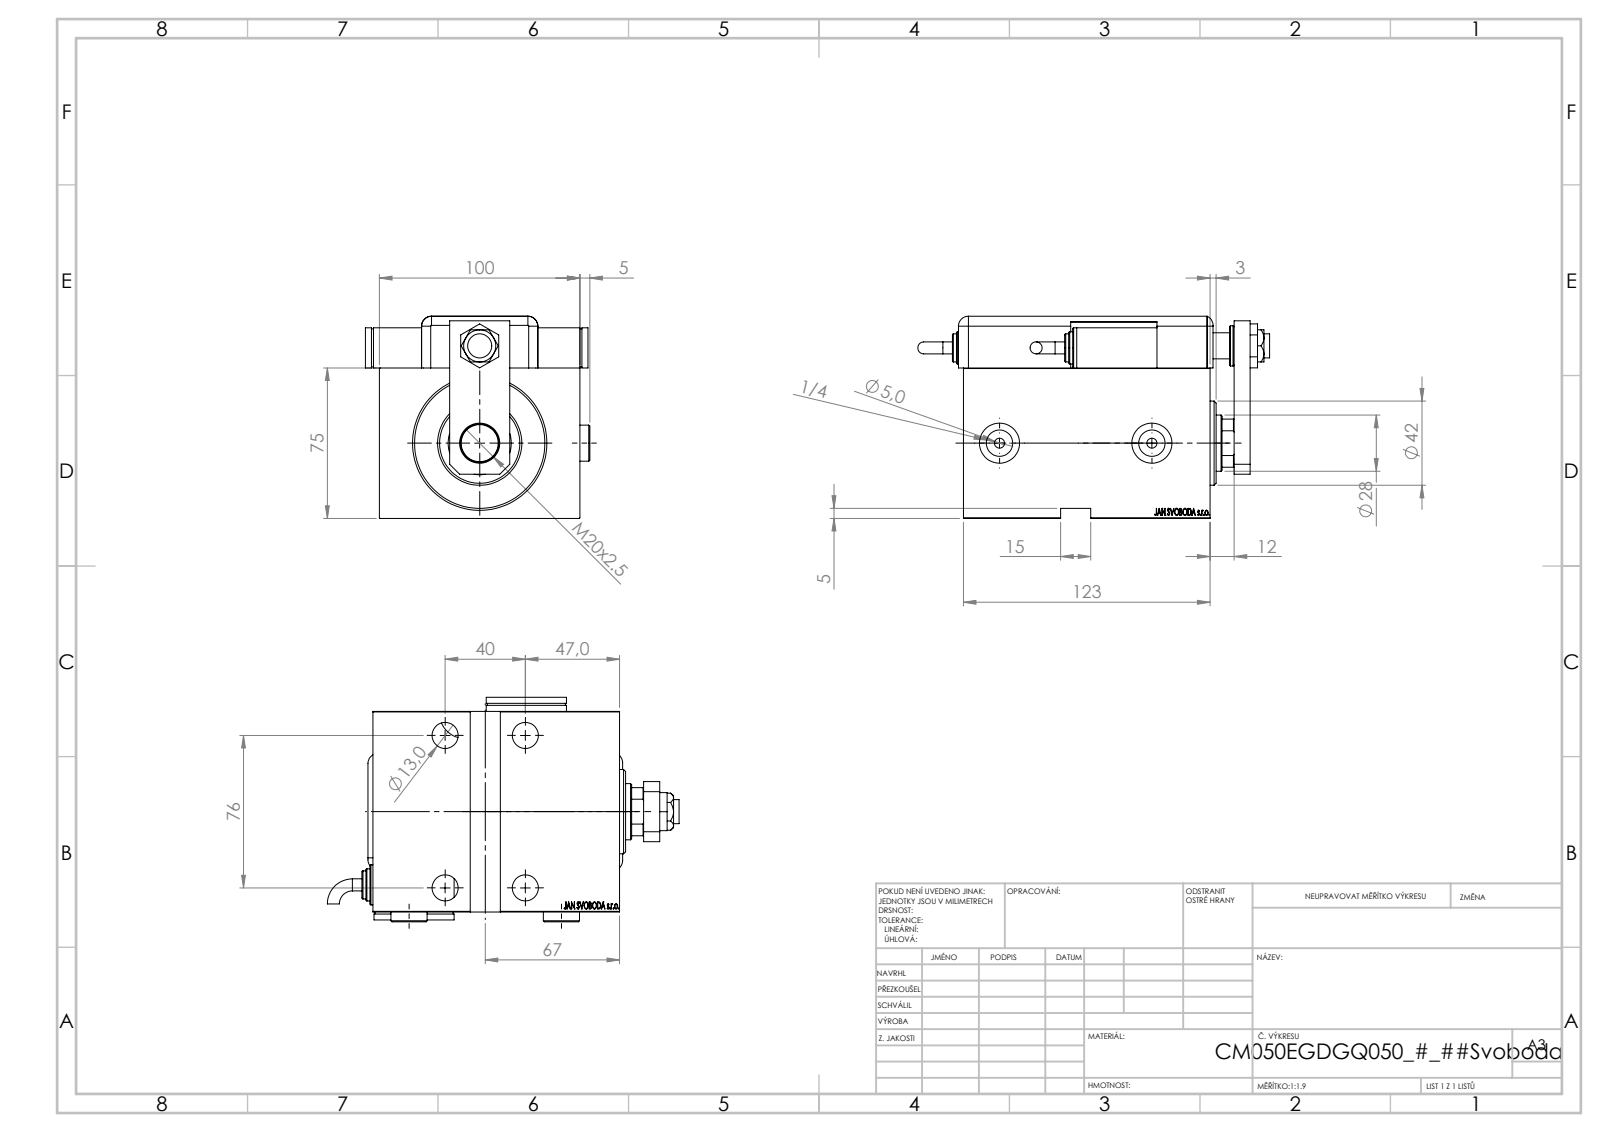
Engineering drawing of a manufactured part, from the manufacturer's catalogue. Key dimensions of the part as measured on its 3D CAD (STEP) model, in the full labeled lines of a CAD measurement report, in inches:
Part name (STEP PRODUCT): NUT_D19; KRYT; SWITCH Q; SWITCH DIM A_G (+8 more)
STEP written by: SolidWorks 2019 (CONFIG_CONTROL_DESIGN)
Units: inches
Bodies: 15 solids, 1296 faces (652 planar, 123 cylindrical, 521 other)
Overall size (bounding box): 6.908 × 4.406 × 3.969
Volume: 58.07 in³ · Surface area: 284.5 in²
Round holes (diameter × count): ⌀0.512 ×5, ⌀0.748 ×4, ⌀0.787 ×3, ⌀0.157 ×2, ⌀0.197 ×2, ⌀0.315 ×2, ⌀0.518 ×2, ⌀0.472 ×1, ⌀0.551 ×1, ⌀0.728 ×1, ⌀1.102 ×1, ⌀1.24 ×1
Round bosses / shafts (diameter × count): ⌀0.787 ×3, ⌀0.709 ×2, ⌀0.63 ×2, ⌀0.551 ×2, ⌀0.236 ×2, ⌀2.047 ×1, ⌀1.654 ×1
Partial cylindrical surfaces — rounded edges, fillets, slot ends (radius × count): R0.197 ×9, R0.394 ×1, R0.531 ×1
Main face-to-face distances: 0.118, 2.953, 3.937, 4.843, 3.969, 1.016, 0.551, 0.787, 4.291, 0.197
Hole centre spacings: 2.992, 1.575, 1.858, 2.41, 3.263, 3.381, 3.606, 0.787
